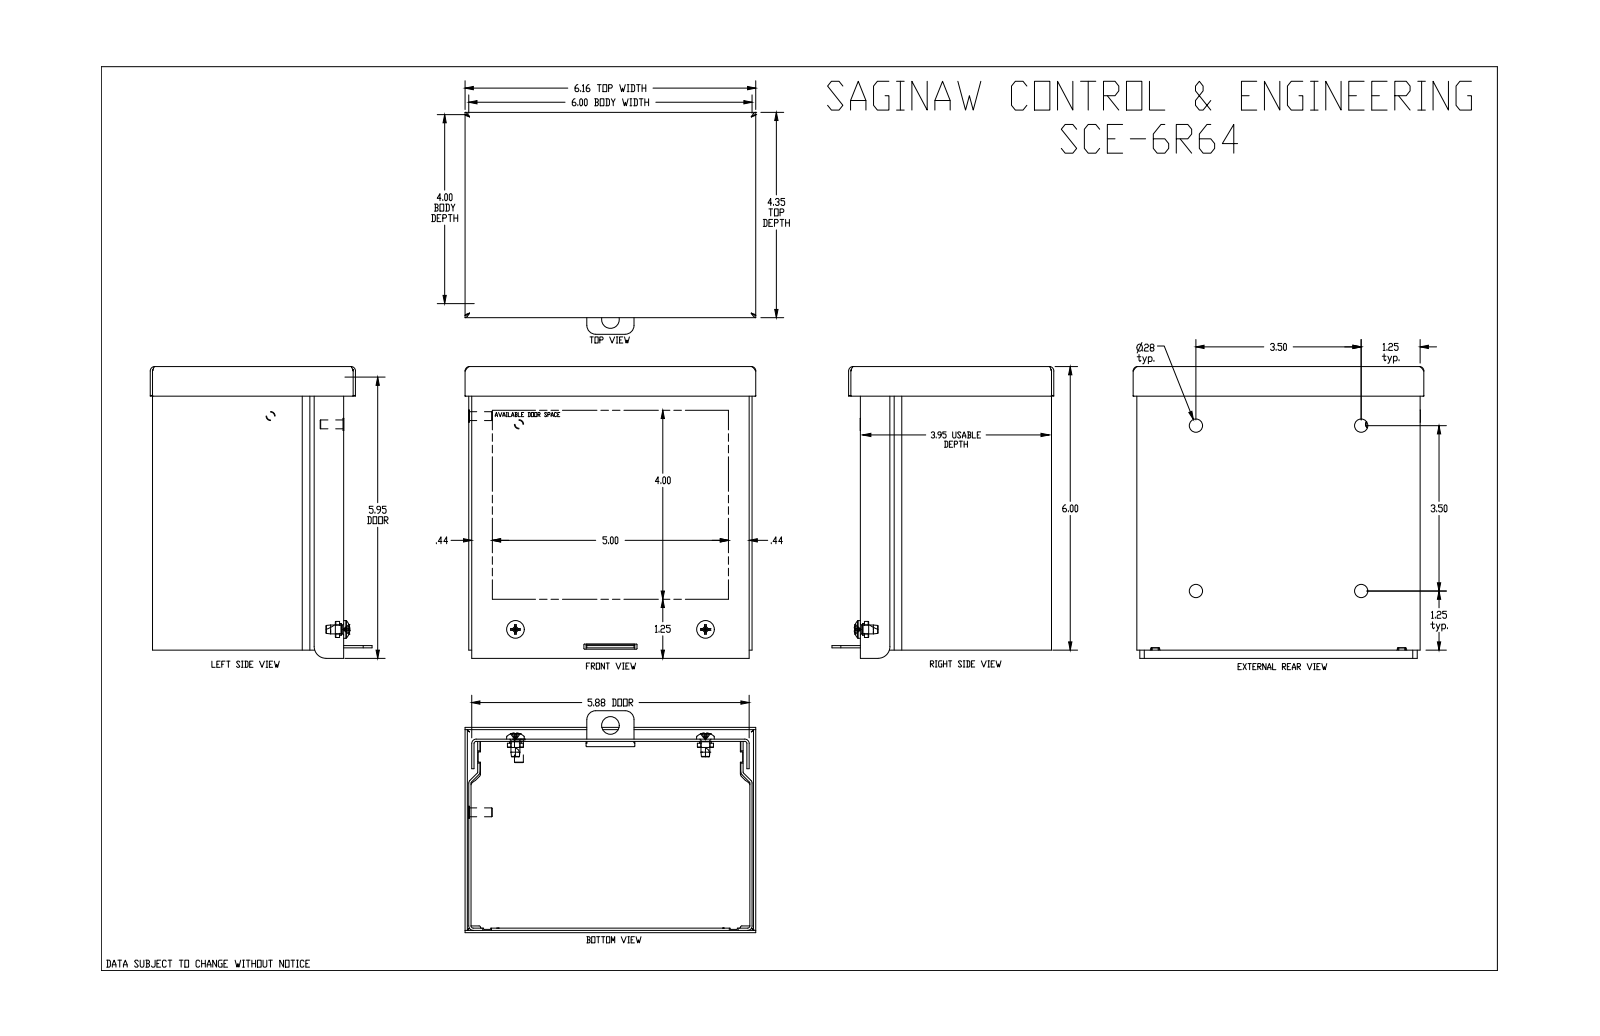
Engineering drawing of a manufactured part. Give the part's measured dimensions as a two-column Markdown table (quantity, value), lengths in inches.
| quantity | value |
| --- | --- |
| part name | SCE-6R64_REV1 |
| STEP written by | SolidWorks 2021 (AUTOMOTIVE_DESIGN) |
| units | inches |
| bodies | 9 solids, 383 faces (193 planar, 158 cylindrical, 32 other) |
| overall size | 6.174 × 6.156 × 4.698 |
| volume | 10.07 in³ |
| surface area | 406.9 in² |
| round holes (diameter × count) | 0.281 × 4, 0.19 × 3, 0.25 × 2, 0.188 × 1, 0.193 × 1, 0.375 × 1 |
| round bosses / shafts (diameter × count) | 0.34 × 2, 0.256 × 2, 0.249 × 2, 0.188 × 2 |
| partial cylindrical surfaces (radius × count) | 0.015 × 32, 0.125 × 12, 0.047 × 8, 0.06 × 8, 0.095 × 8, 0.025 × 4, 0.073 × 4, 0.062 × 3 |
| main face-to-face distances | 0.048, 4.01, 5.952, 3.962, 6, 0.06, 4.058, 5.904, 5.892, 5.94 |
| hole center spacings | 3.5, 0.854, 3.848, 4.32, 4.95, 5.723, 0.189, 1.344 |
